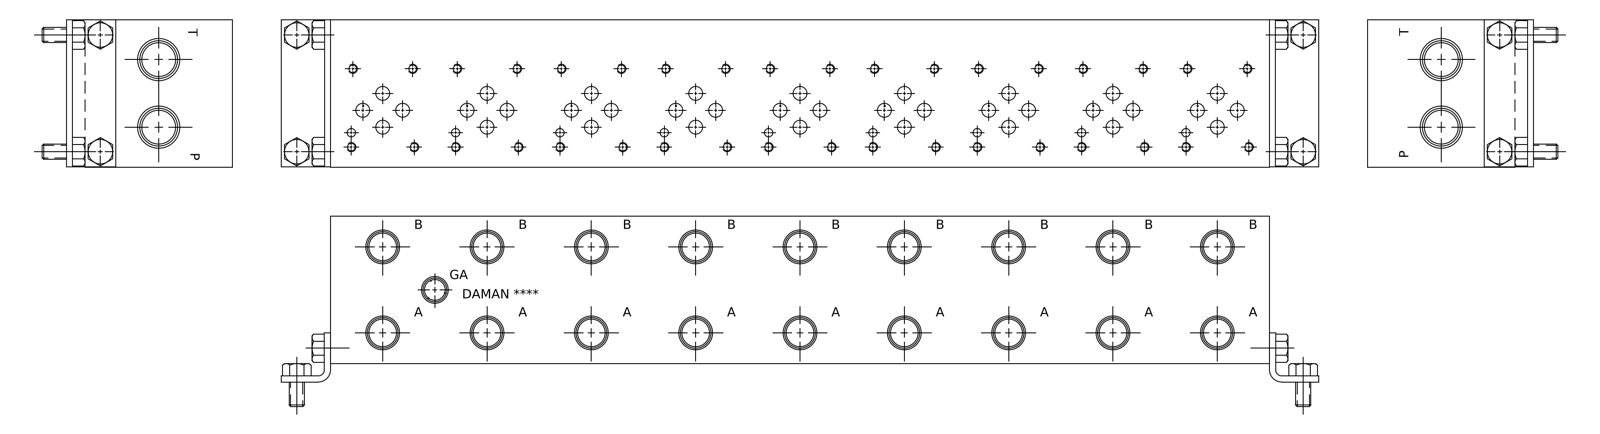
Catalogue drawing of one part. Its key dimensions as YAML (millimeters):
part_name: "Part_AD03P092P_3D"
step_written_by: "Autodesk Inventor 2019 (AUTOMOTIVE_DESIGN)"
units: millimeters
bodies: {solids: 1, faces: 1116, planar: 568, cylindrical: 175, other: 373}
overall_size: [485.77, 76.2, 76.2]
volume: 2705000
surface_area: 196269
round_holes:
  - {diameter: 3.78, count: 36}
  - {diameter: 4.83, count: 36}
  - {diameter: 7.14, count: 27}
  - {diameter: 14.3, count: 18}
  - {diameter: 17.3, count: 18}
  - {diameter: 3.96, count: 9}
  - {diameter: 6.35, count: 9}
  - {diameter: 6.53, count: 3}
  - {diameter: 7.92, count: 3}
  - {diameter: 15.88, count: 2}
  - {diameter: 17.48, count: 2}
  - {diameter: 21.59, count: 2}
face_to_face_distances: [76.2, 485.77, 11.73, 64.47, 1, 10.73, 75.2, 60.2, 16, 15.37]
hole_center_spacings: [107.95, 215.9, 53.98, 161.93, 53.97, 116.74, 161.92, 269.88]
